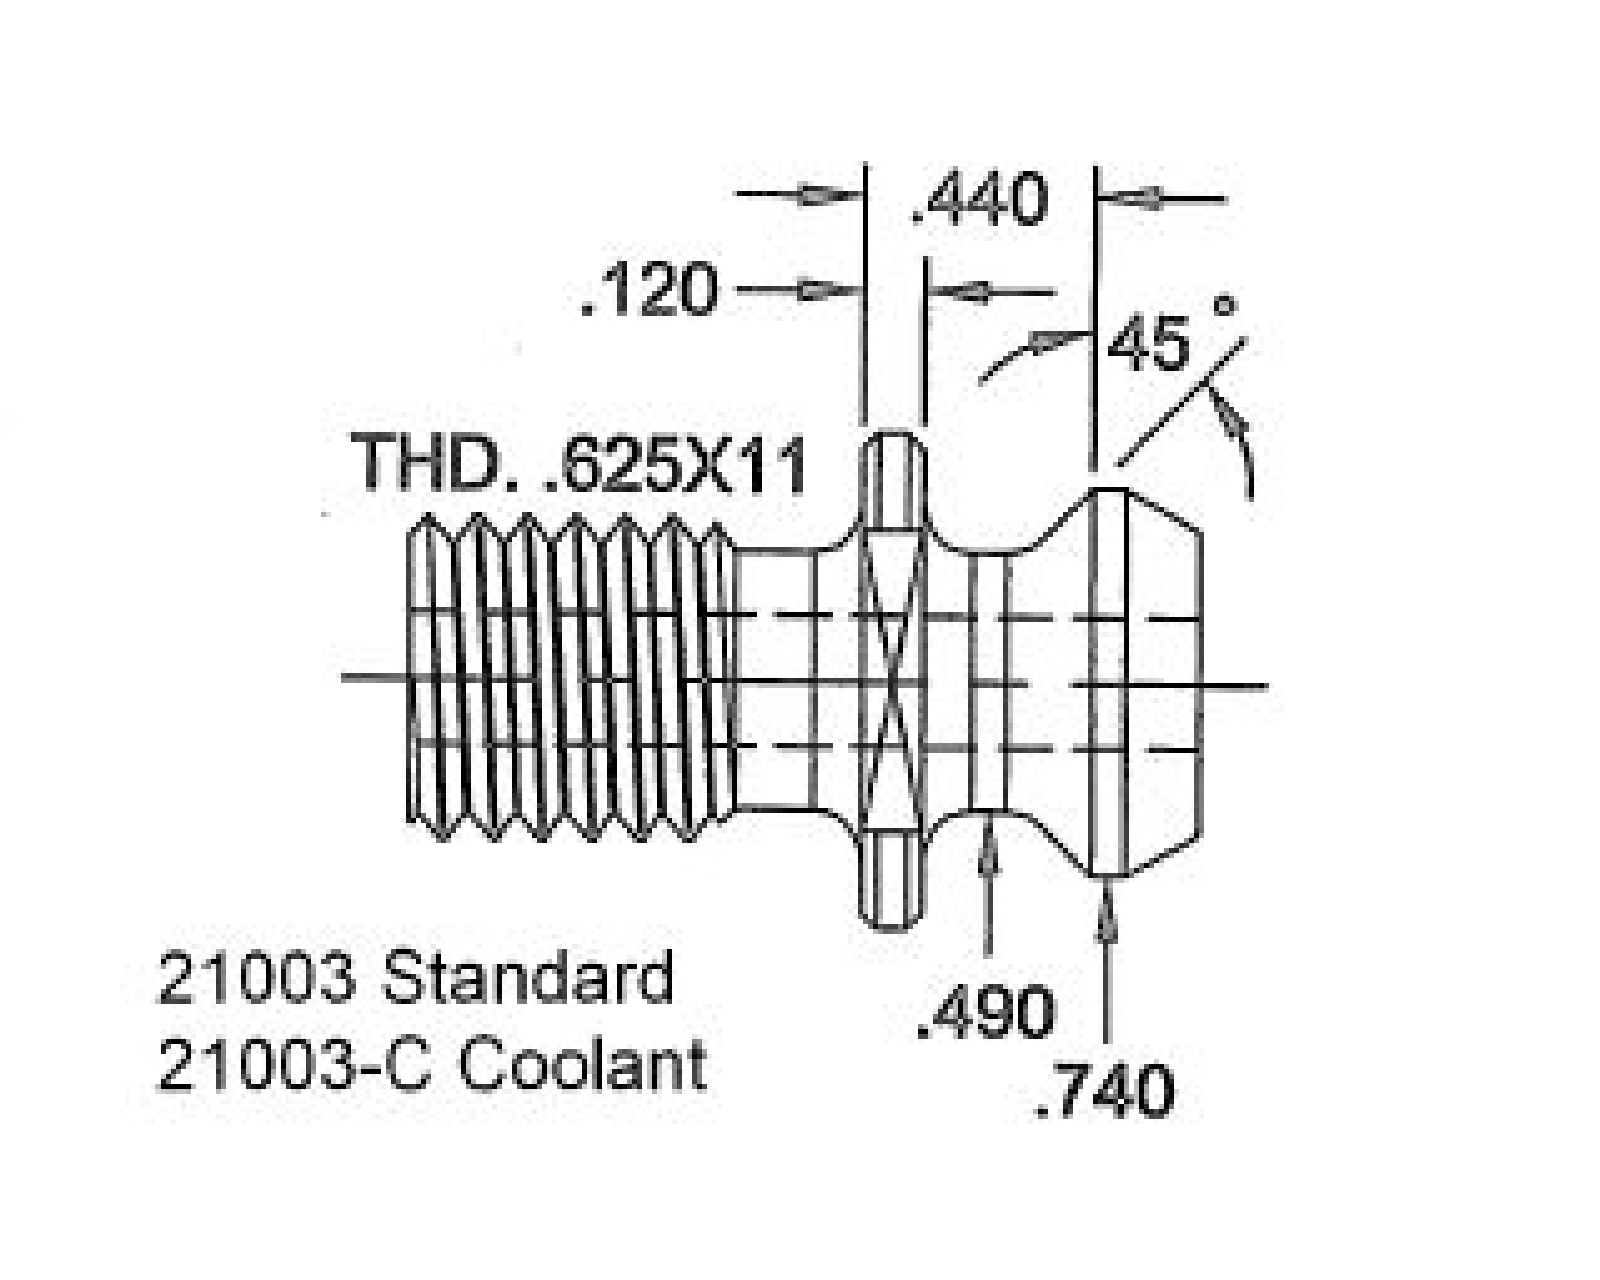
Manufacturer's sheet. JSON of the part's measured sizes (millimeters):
{"part_name": "STP-21003-45C", "step_written_by": "SolidWorks 2015 (CONFIG_CONTROL_DESIGN)", "units": "millimeters", "bodies": {"solids": 1, "faces": 32, "planar": 8, "cylindrical": 12, "other": 12}, "overall_size": [57.15, 23, 23], "volume_mm3": 8679, "surface_area_mm2": 4152, "round_holes": [[4, 1]], "round_bosses_or_shafts": [[23, 1], [15.88, 1], [15, 1], [13, 1], [10, 1]], "face_to_face_distances": [28.49, 6, 22.49, 28.66, 34.66, 57.15, 19.06, 32.66, 4, 2]}
